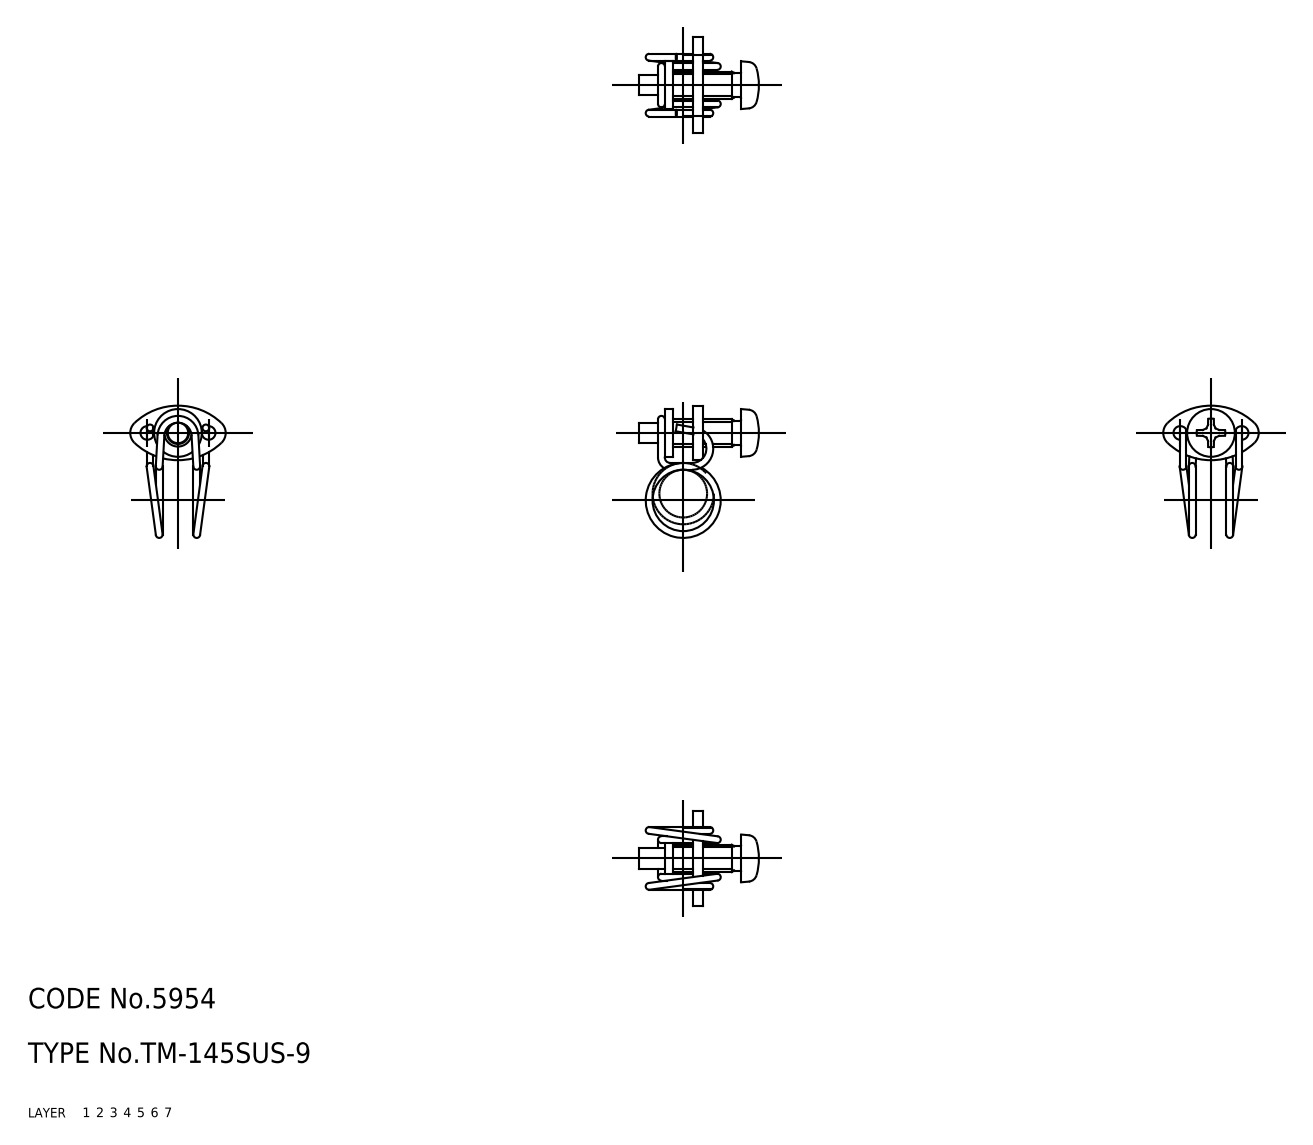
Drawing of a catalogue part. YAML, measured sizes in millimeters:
part_name: "screw; holder; band; TM_145SUS_9_23006_36"
step_written_by: "CADfix (AUTOMOTIVE_DESIGN)"
units: millimeters
bodies: {solids: 3, faces: 85, planar: 0, cylindrical: 0, other: 85}
overall_size: [19.4, 17.55, 14]
volume: 451
surface_area: 925
